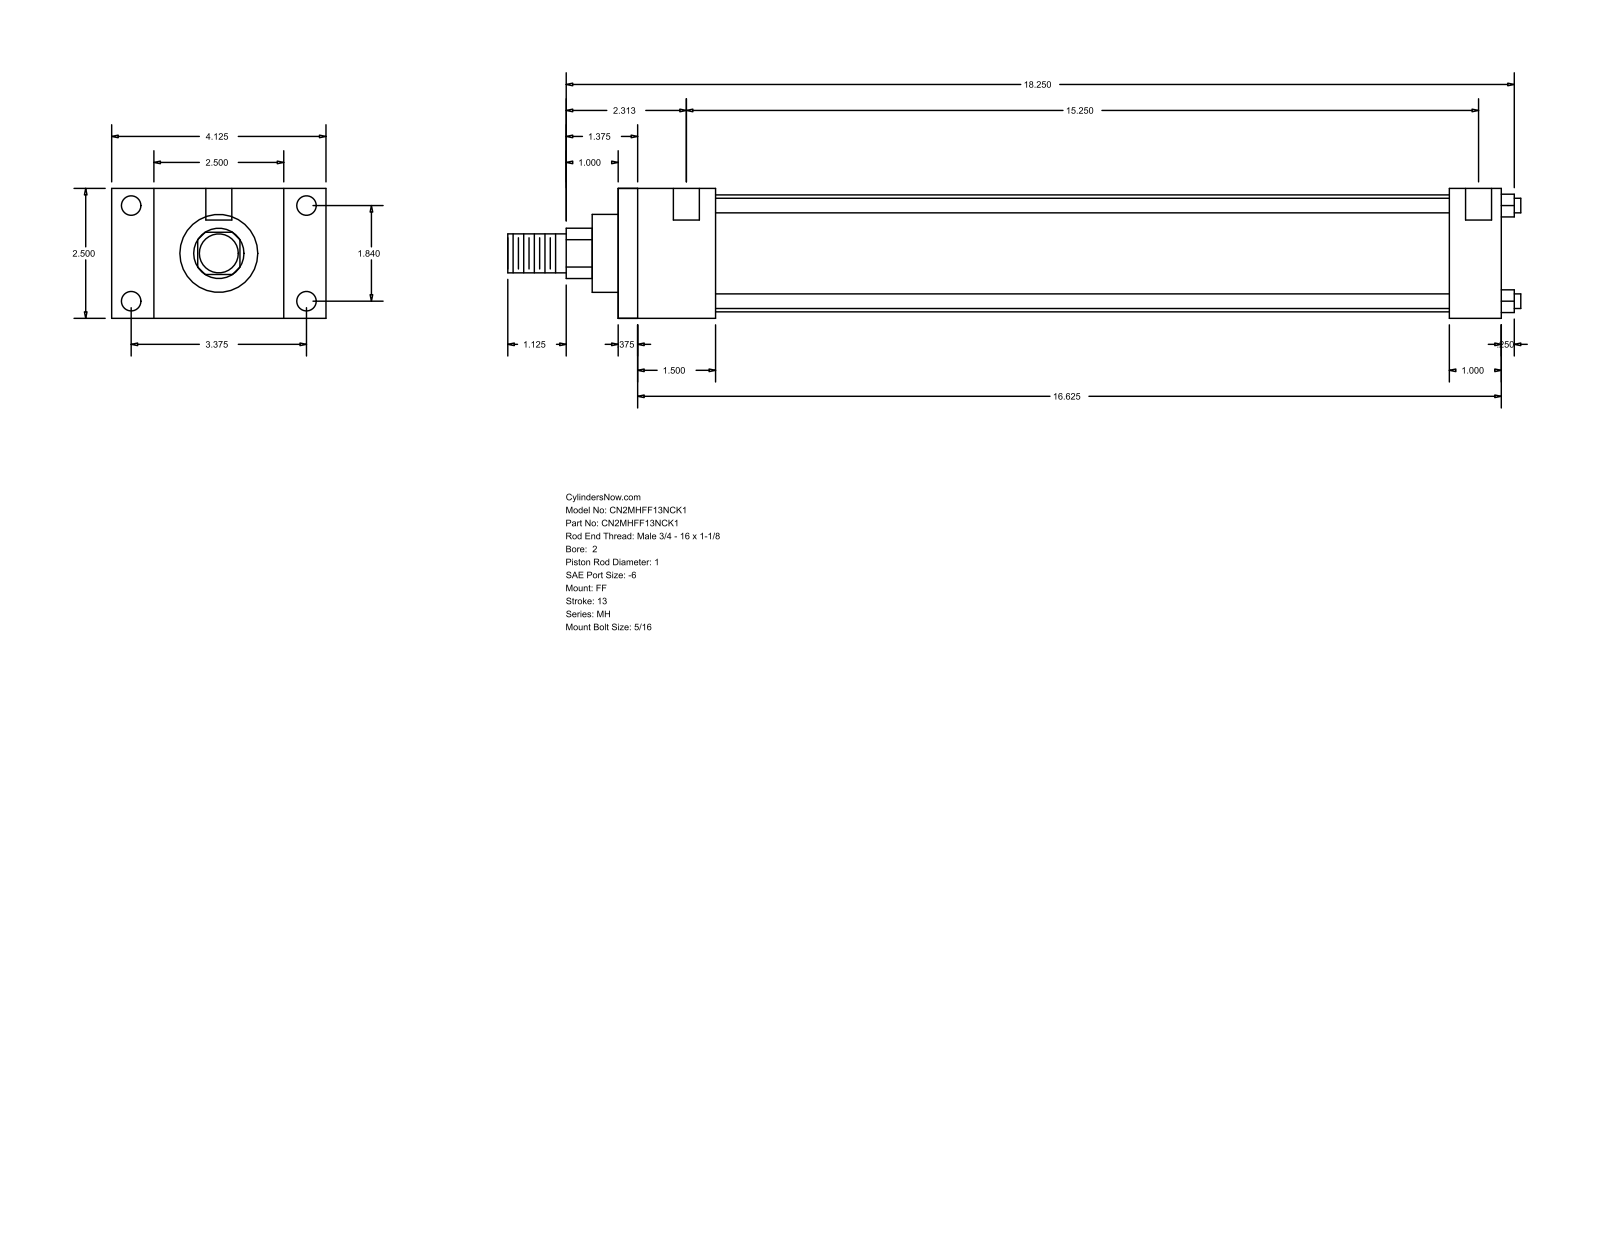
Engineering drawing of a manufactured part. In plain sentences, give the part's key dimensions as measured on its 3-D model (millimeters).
The part is named "MH_FF__0200_1". Its 3-D file was written by "GSSL Pune (CONFIG_CONTROL_DESIGN)". It is 0 solids with 92 faces: 64 planar, 28 cylindrical and 0 other. Overall it measures 495.3 by 104.78 by 63.5 millimeters. Round holes: 4 of diameter 5.56, 4 of diameter 9.53, 2 of diameter 12.7. Round bosses or shafts: 4 of diameter 7.14, 1 of diameter 57.15, 1 of diameter 38.1, 1 of diameter 25.4, 1 of diameter 19.05. Partial cylindrical surfaces (rounded edges, fillets, slot ends): 1 of radius 12.29. The main face-to-face distances are 63.5, 431.8, 9.52, 422.28, 20.64, 25.4, 47.63, 406.4, 38.11, 396.88. The hole center spacings are 46.74, 85.72, 97.63, 395.28, 3.17, 4.76, 387.35, 390.52.
